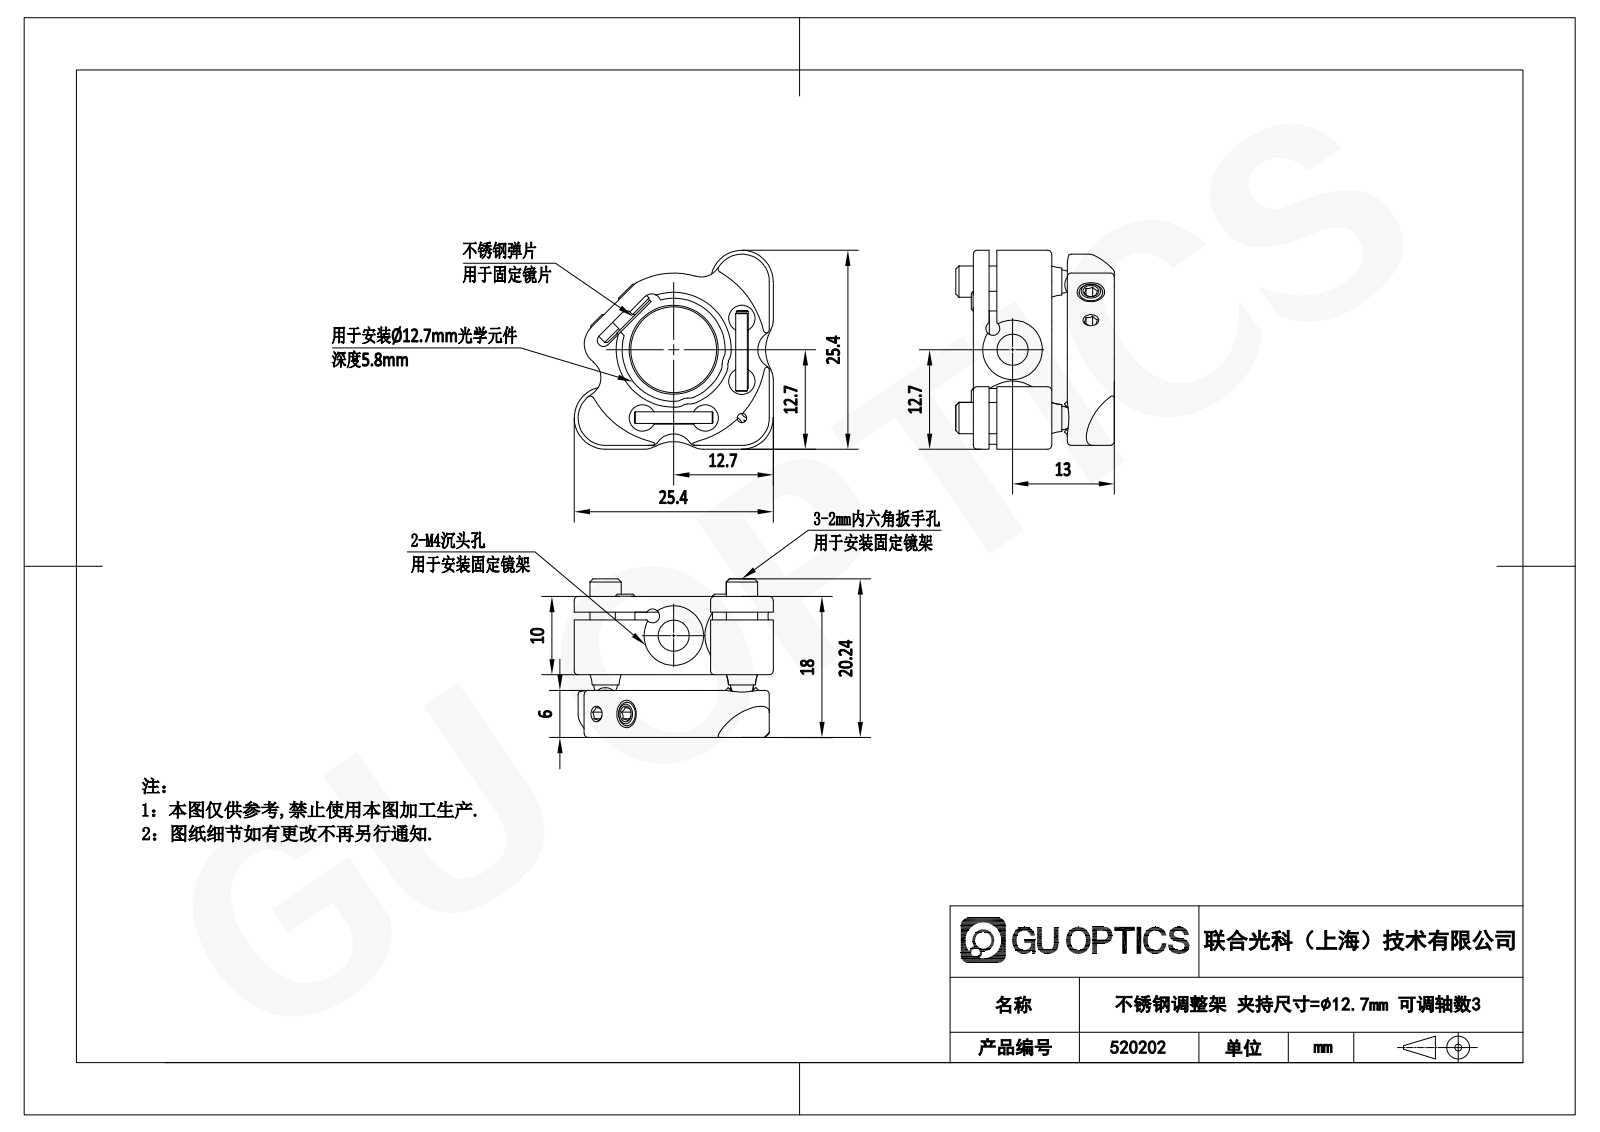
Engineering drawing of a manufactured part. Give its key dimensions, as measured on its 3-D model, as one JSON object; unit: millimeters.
{"part_name": "520202", "step_written_by": "SolidWorks 2020 (CONFIG_CONTROL_DESIGN)", "units": "millimeters", "bodies": {"solids": 0, "faces": 349, "planar": 120, "cylindrical": 120, "other": 109}, "overall_size": [25.4, 25.4, 20.24], "round_holes": [[2.5, 2], [1.2, 1], [11, 1]], "round_bosses_or_shafts": [[2.5, 7], [4, 5], [3.4, 4], [1.5, 4], [1.8, 3], [7.6, 2], [2, 2], [3, 1]], "partial_cylinders_radius": [[0.5, 17], [2.5, 6], [1, 5], [1.5, 4], [3.5, 3], [4, 3], [0.8, 2], [1.15, 2]], "face_to_face_distances": [2, 10, 8, 6, 1, 3, 12, 7, 9, 15], "hole_center_spacings": [12.3]}
